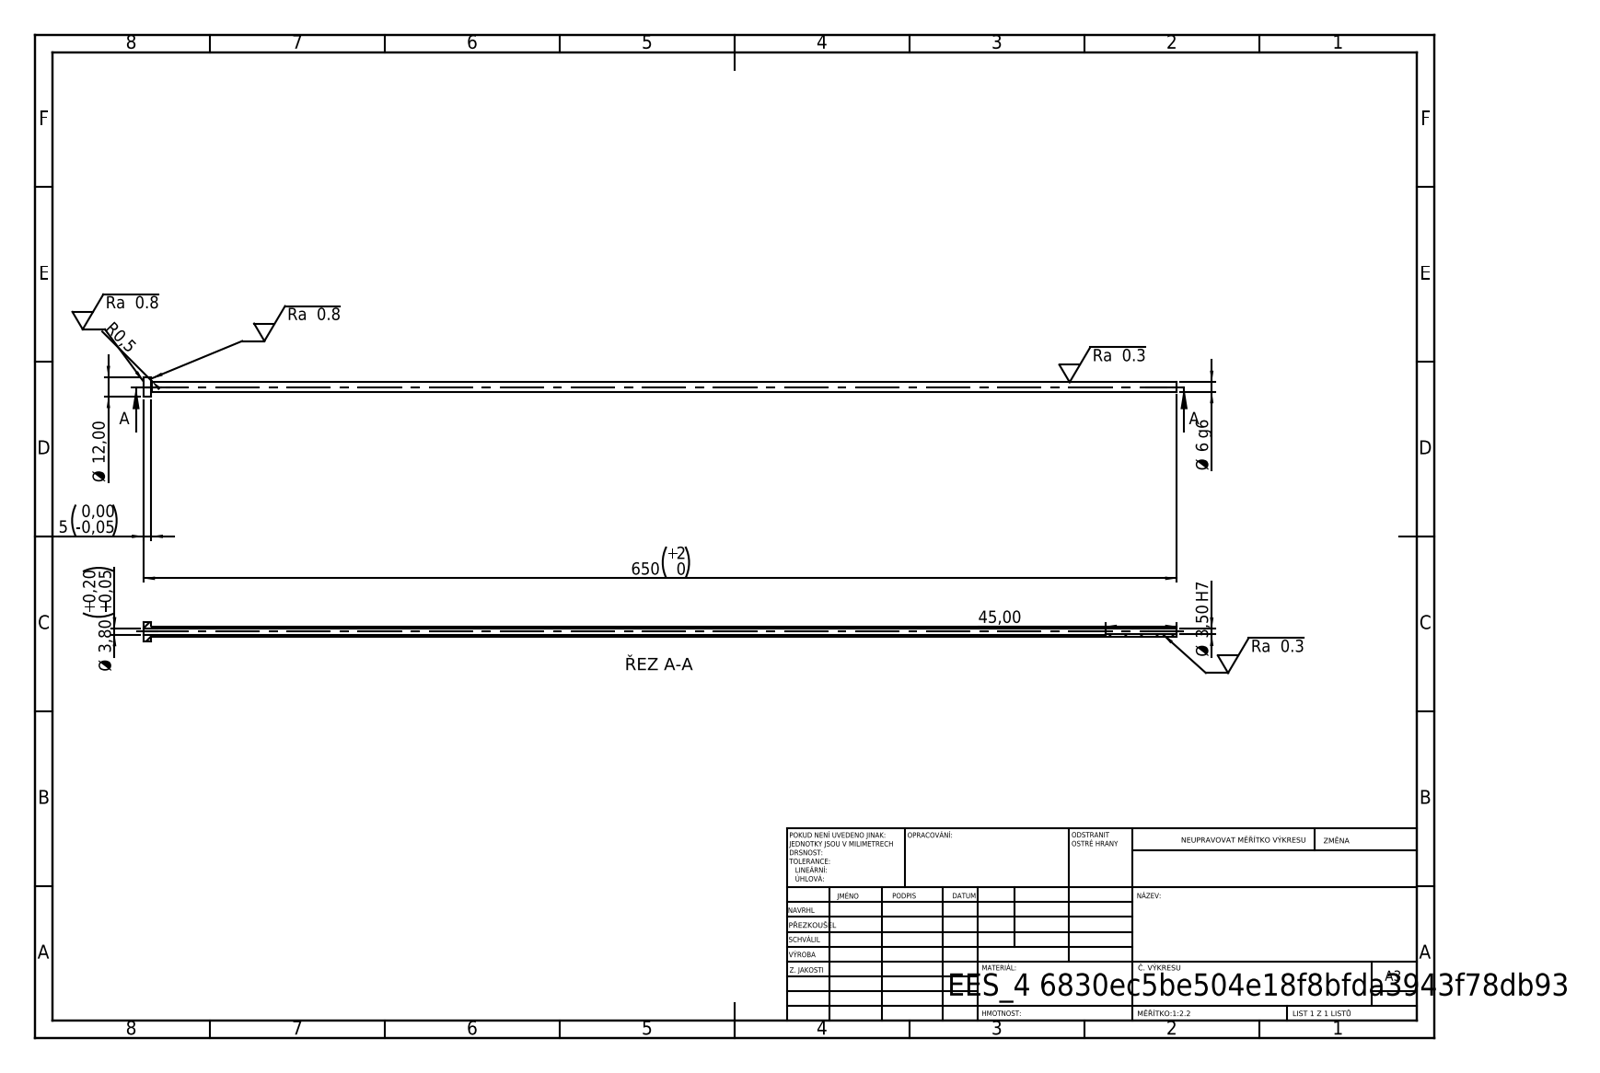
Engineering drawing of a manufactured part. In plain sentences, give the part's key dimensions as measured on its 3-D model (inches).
Its 3-D file was written by "SolidWorks 2019 (CONFIG_CONTROL_DESIGN)". It is 1 solid with 14 faces: 4 planar, 8 cylindrical and 2 other. Overall it measures 25.591 by 0.472 by 0.472 inches. Its volume is 0.702 cubic inches and its surface area 31.41 square inches. Round holes: 1 of diameter 0.138, 1 of diameter 0.15. Round bosses or shafts: 1 of diameter 0.472, 1 of diameter 0.236. The main face-to-face distances are 0.197, 25.591, 25.394, 23.819, 23.622, 1.772.
